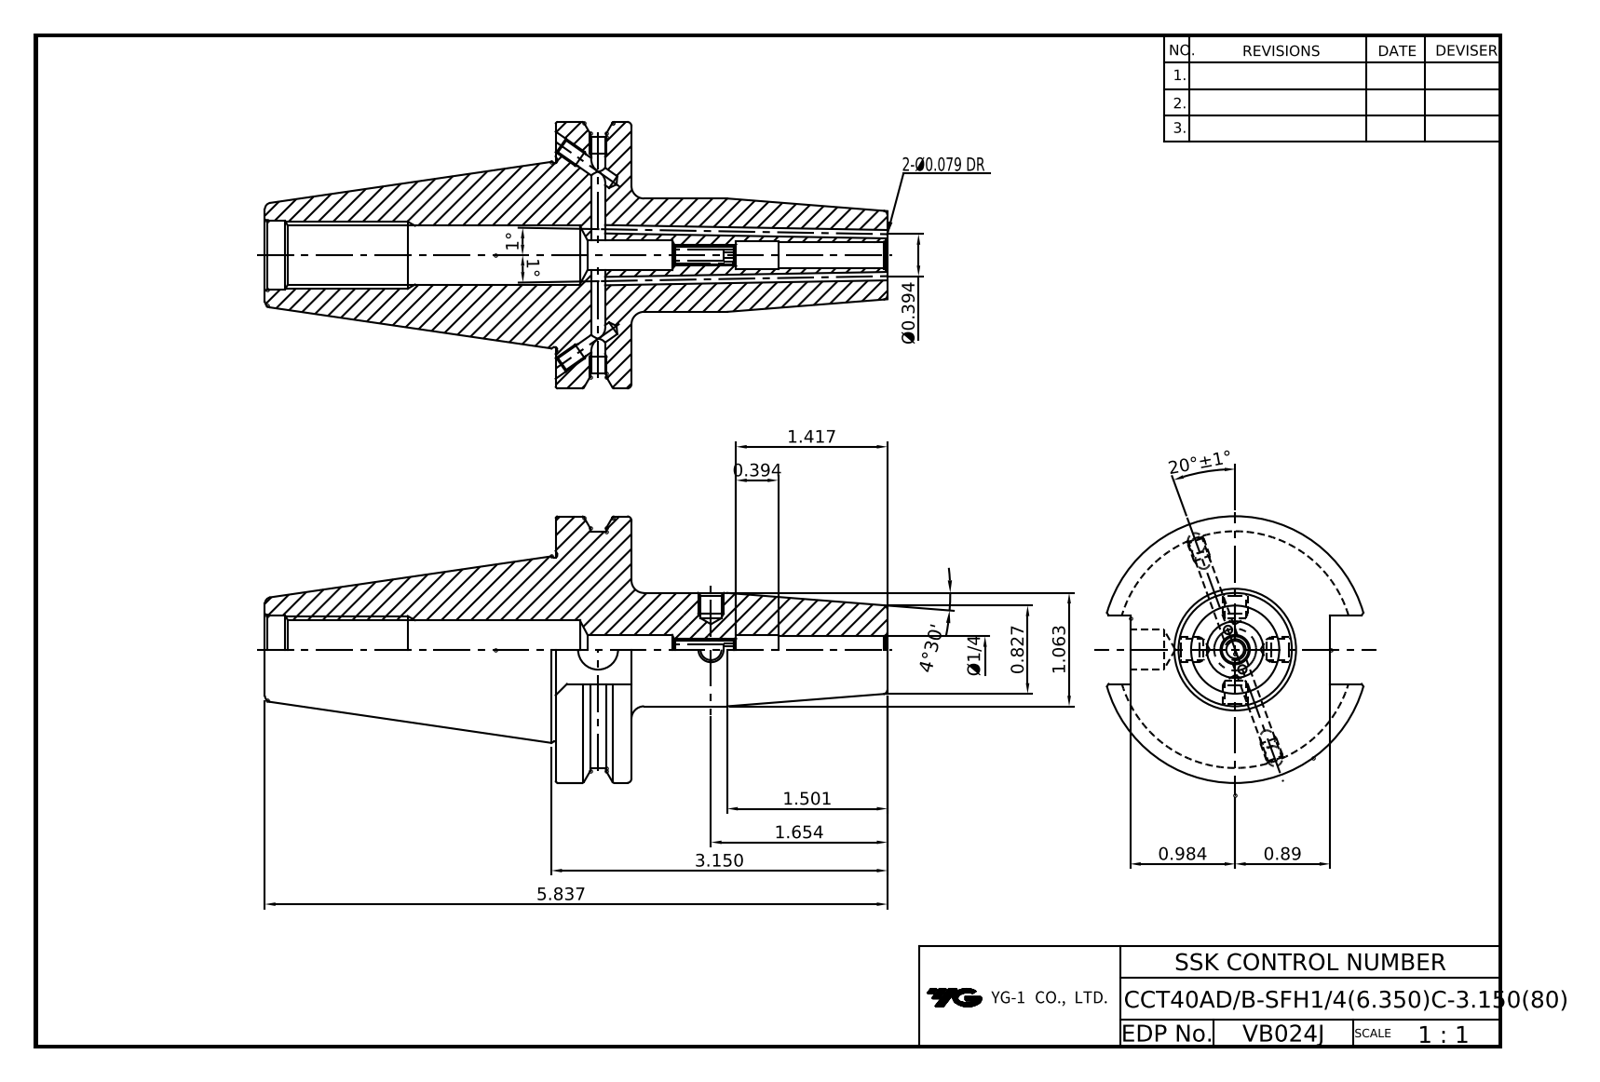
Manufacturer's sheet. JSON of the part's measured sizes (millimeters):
{"part_name": "LO-CCT40ADB-SFH1_4C-3_15", "step_written_by": "CREO PARAMETRIC BY PTC INC, 2018100 (CONFIG_CONTROL_DESIGN)", "units": "millimeters", "bodies": {"solids": 1, "faces": 152, "planar": 48, "cylindrical": 64, "other": 40}, "overall_size": [148.25, 63.5, 61], "volume_mm3": 132677, "surface_area_mm2": 28568, "round_holes": [[4, 7], [3.4, 3], [4.2, 1], [5, 1], [6.35, 1], [6.75, 1], [7, 1], [9.53, 1], [13.5, 1], [14, 1], [15.88, 1], [16.3, 1]], "round_bosses_or_shafts": [[63.5, 1], [43.8, 1], [27, 1]], "partial_cylinders_radius": [[28.15, 1]], "face_to_face_distances": [18.05, 79, 60.95, 47.6, 69.25, 87.3, 148.25, 16.38, 4.8, 64.45]}
